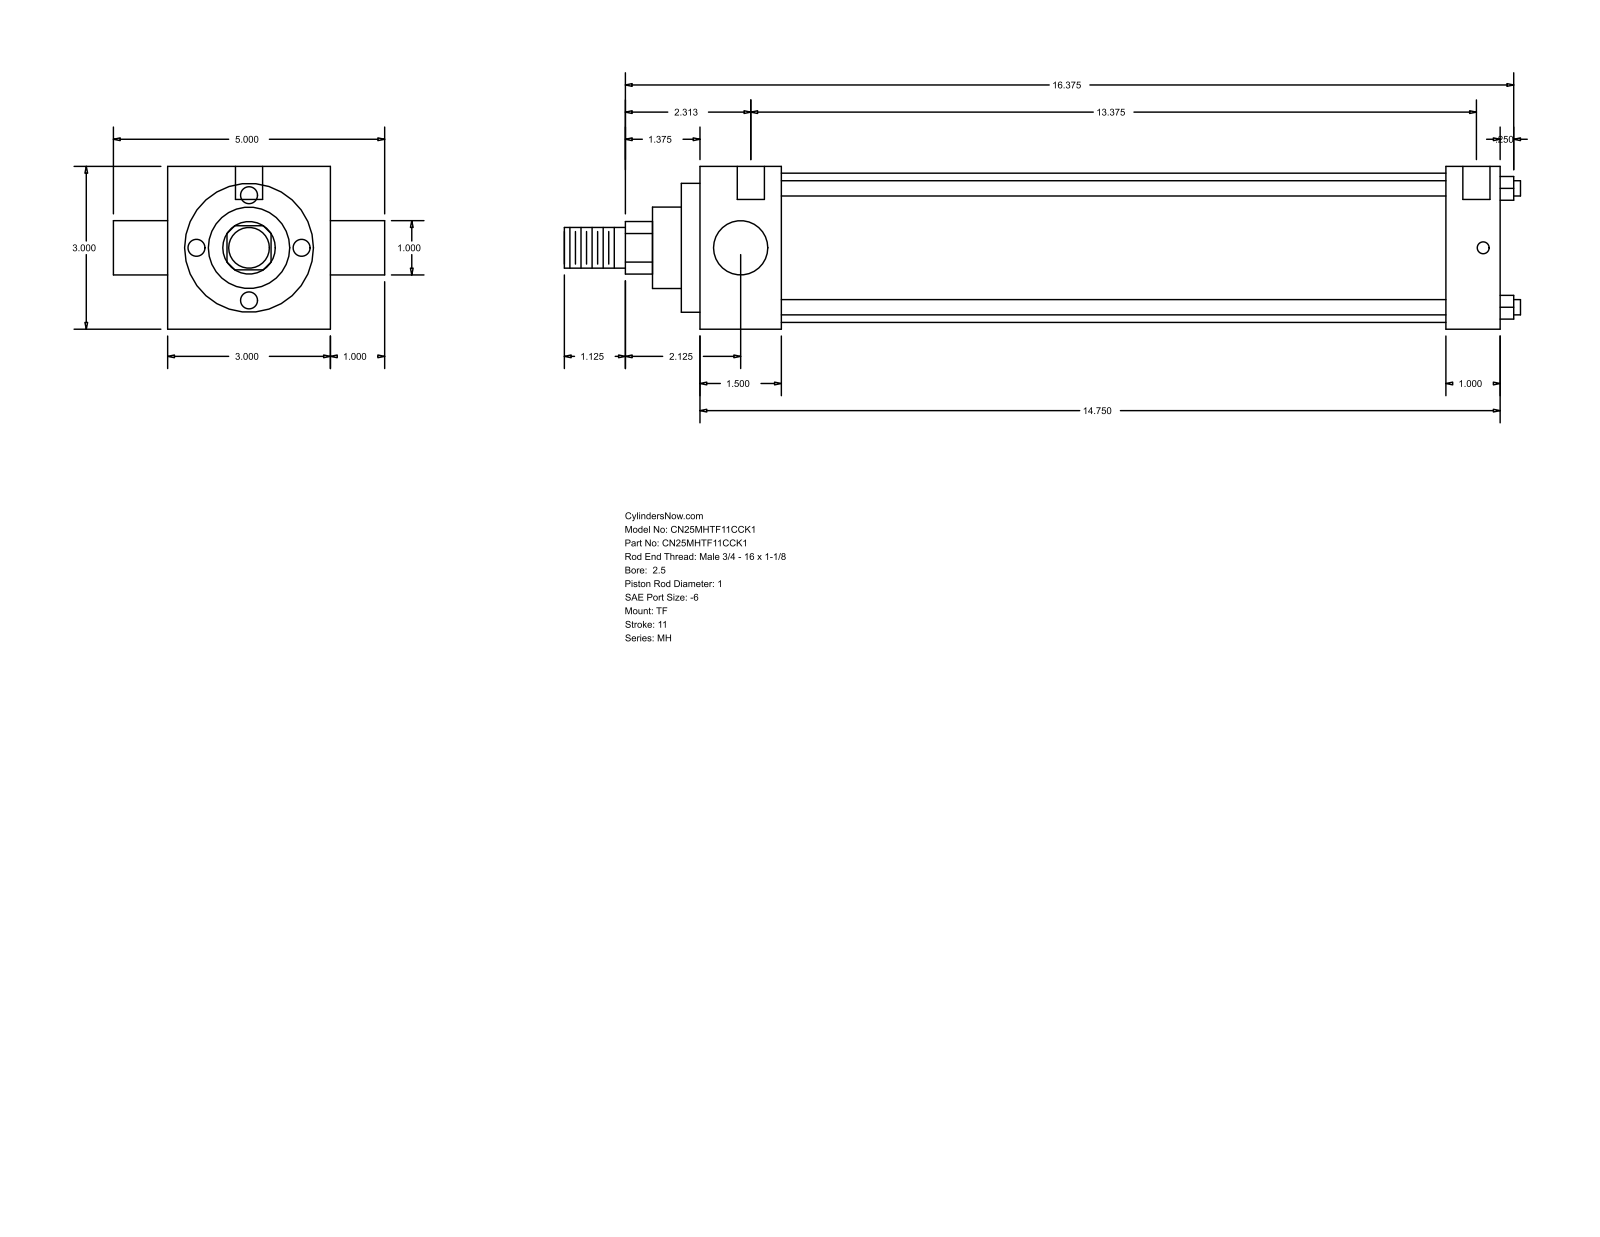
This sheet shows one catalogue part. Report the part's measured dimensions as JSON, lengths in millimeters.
{"part_name": "MH_TF__0250_1", "step_written_by": "GSSL Pune (CONFIG_CONTROL_DESIGN)", "units": "millimeters", "bodies": {"solids": 0, "faces": 86, "planar": 61, "cylindrical": 25, "other": 0}, "overall_size": [447.68, 127, 76.2], "round_holes": [[5.56, 3], [12.7, 2]], "round_bosses_or_shafts": [[7.14, 4], [25.4, 2], [69.85, 1], [60.33, 1], [38.1, 1], [19.05, 1]], "partial_cylinders_radius": [[12.29, 1]], "face_to_face_distances": [76.2, 374.65, 25.39, 38.11, 336.54, 349.26, 311.15, 8.73, 46.84, 357.99], "hole_center_spacings": [3.18, 4.76, 339.72, 342.9, 344.48, 347.66]}
